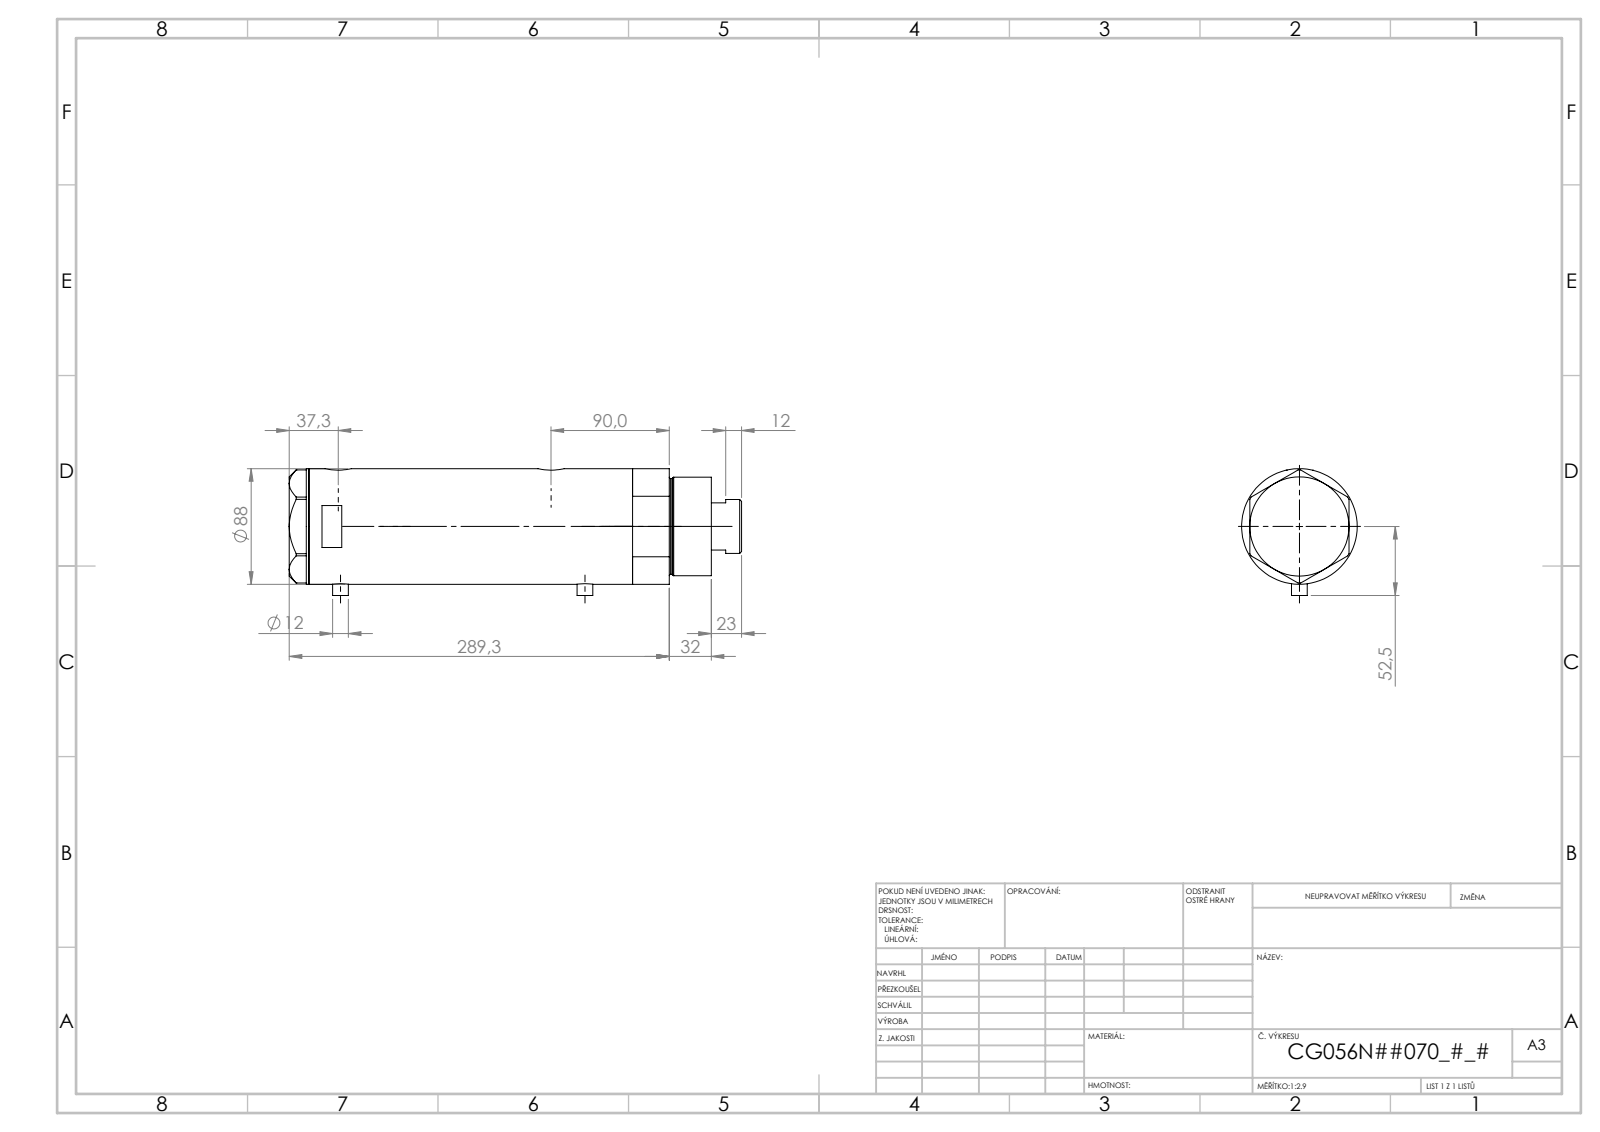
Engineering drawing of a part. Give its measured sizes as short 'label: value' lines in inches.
name: V270CG_MIDDLE; V270CG_VC; V270CG_FRONT; V270CG_BACK
written by: SolidWorks 2019 (CONFIG_CONTROL_DESIGN)
unit: in
bodies: 4 solids, 126 faces (53 planar, 53 cylindrical, 20 other)
size: 11.593 × 3.508 × 3.465
volume: 92.27 in³; area: 342.8 in²
holes: 2× ⌀0.197, 2× ⌀0.492, 2× ⌀0.518, 2× ⌀0.787, 1× ⌀0.571, 1× ⌀1.654, 1× ⌀1.713, 1× ⌀2.205, 1× ⌀2.362, 1× ⌀3.15
bosses: 2× ⌀0.472, 1× ⌀3.465, 1× ⌀2.953, 1× ⌀2.874, 1× ⌀1.614
face distances: 5.685, 1.024, 4.661, 0.591, 1.614, 6.276, 10.097, 10.688, 9.074, 4.412
hole spacings: 0.067, 1.016, 4.736, 4.803, 5.752, 5.819
